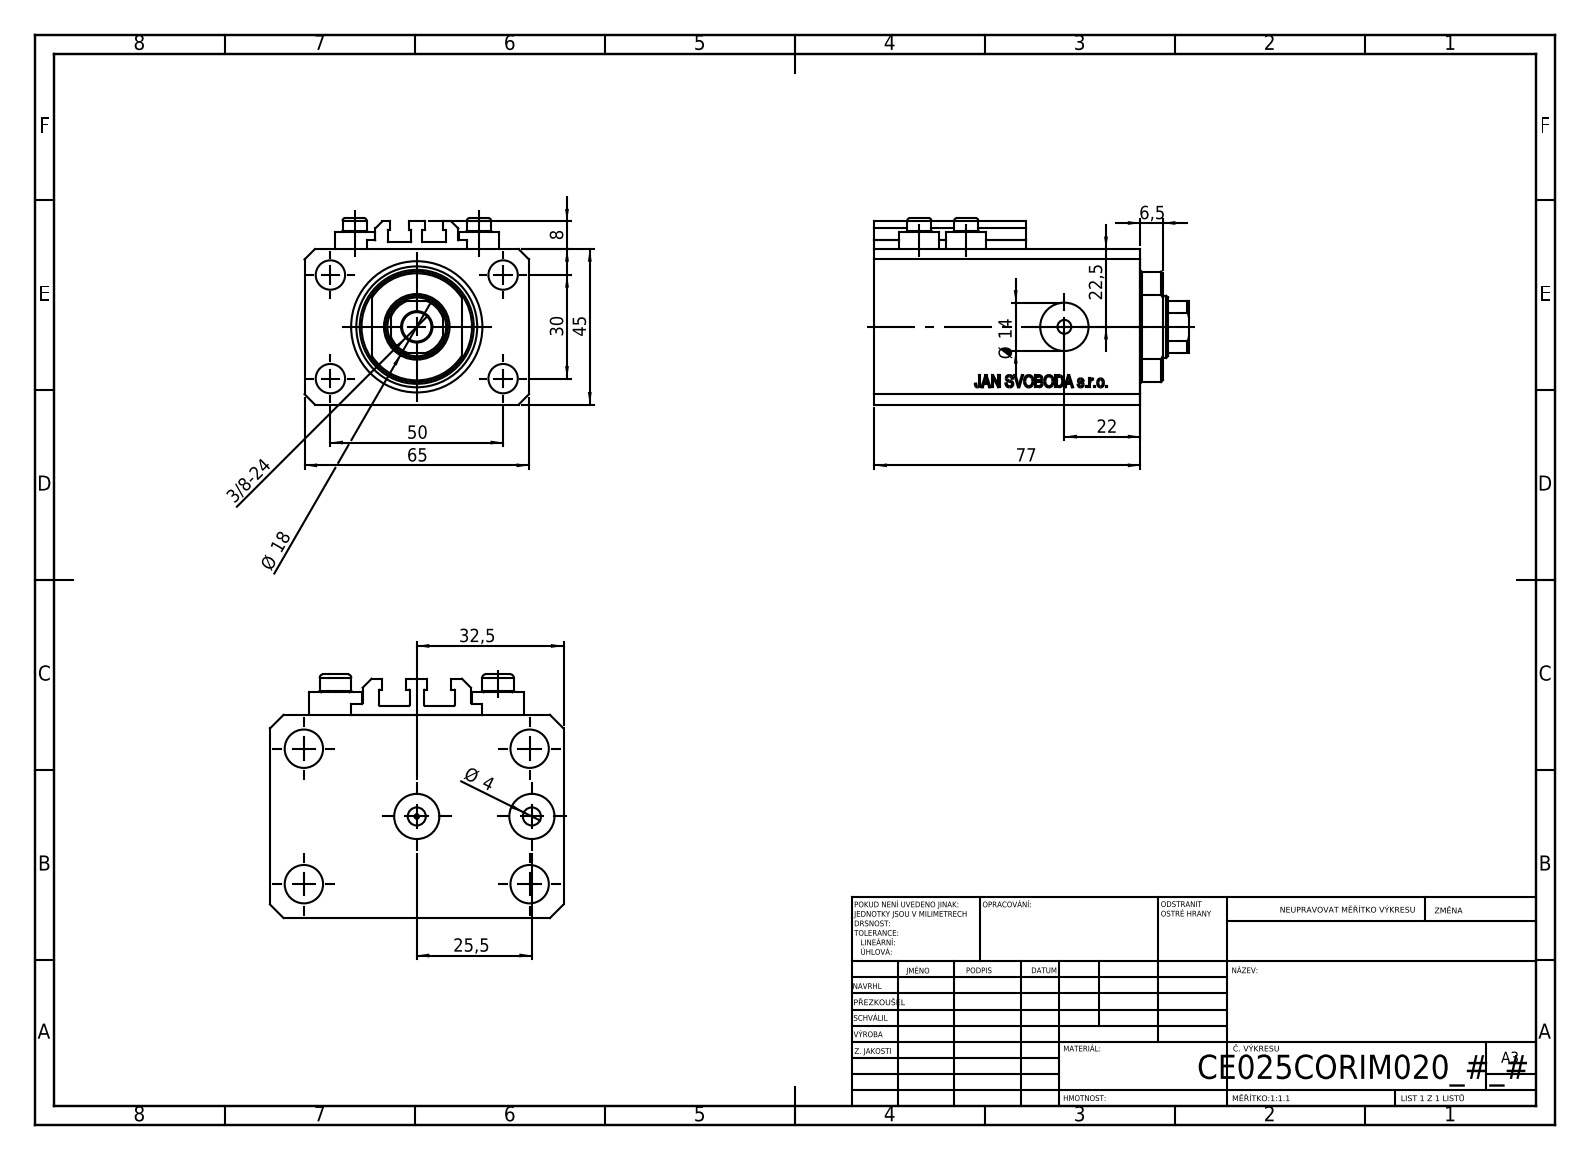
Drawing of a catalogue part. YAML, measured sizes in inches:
part_name: "V250CE_C_VCP; V250CE_C_Body; ALLEN BOLT V250CE; V250CE_VC_C"
step_written_by: "SolidWorks 2019 (CONFIG_CONTROL_DESIGN)"
units: inches
bodies: {solids: 8, faces: 1042, planar: 504, cylindrical: 92, other: 446}
overall_size: [3.583, 2.559, 2.126]
volume: 12.91
surface_area: 89.4
round_holes:
  - {diameter: 0.157, count: 8}
  - {diameter: 0.335, count: 5}
  - {diameter: 0.394, count: 2}
  - {diameter: 0.551, count: 2}
  - {diameter: 0.049, count: 1}
  - {diameter: 0.709, count: 1}
  - {diameter: 0.984, count: 1}
  - {diameter: 1.496, count: 1}
round_bosses_or_shafts:
  - {diameter: 0.457, count: 4}
  - {diameter: 0.276, count: 4}
partial_cylinders:
  - {radius: 0.008, count: 10}
  - {radius: 0.335, count: 1}
  - {radius: 0.63, count: 1}
face_to_face_distances: [1.772, 2.559, 0.551, 3.031, 2.48, 0.272, 2.209, 2.76, 0.118, 1.85]
hole_center_spacings: [1.148, 0.535, 0.591, 1.181, 1.417, 1.515, 1.969, 2.074]
